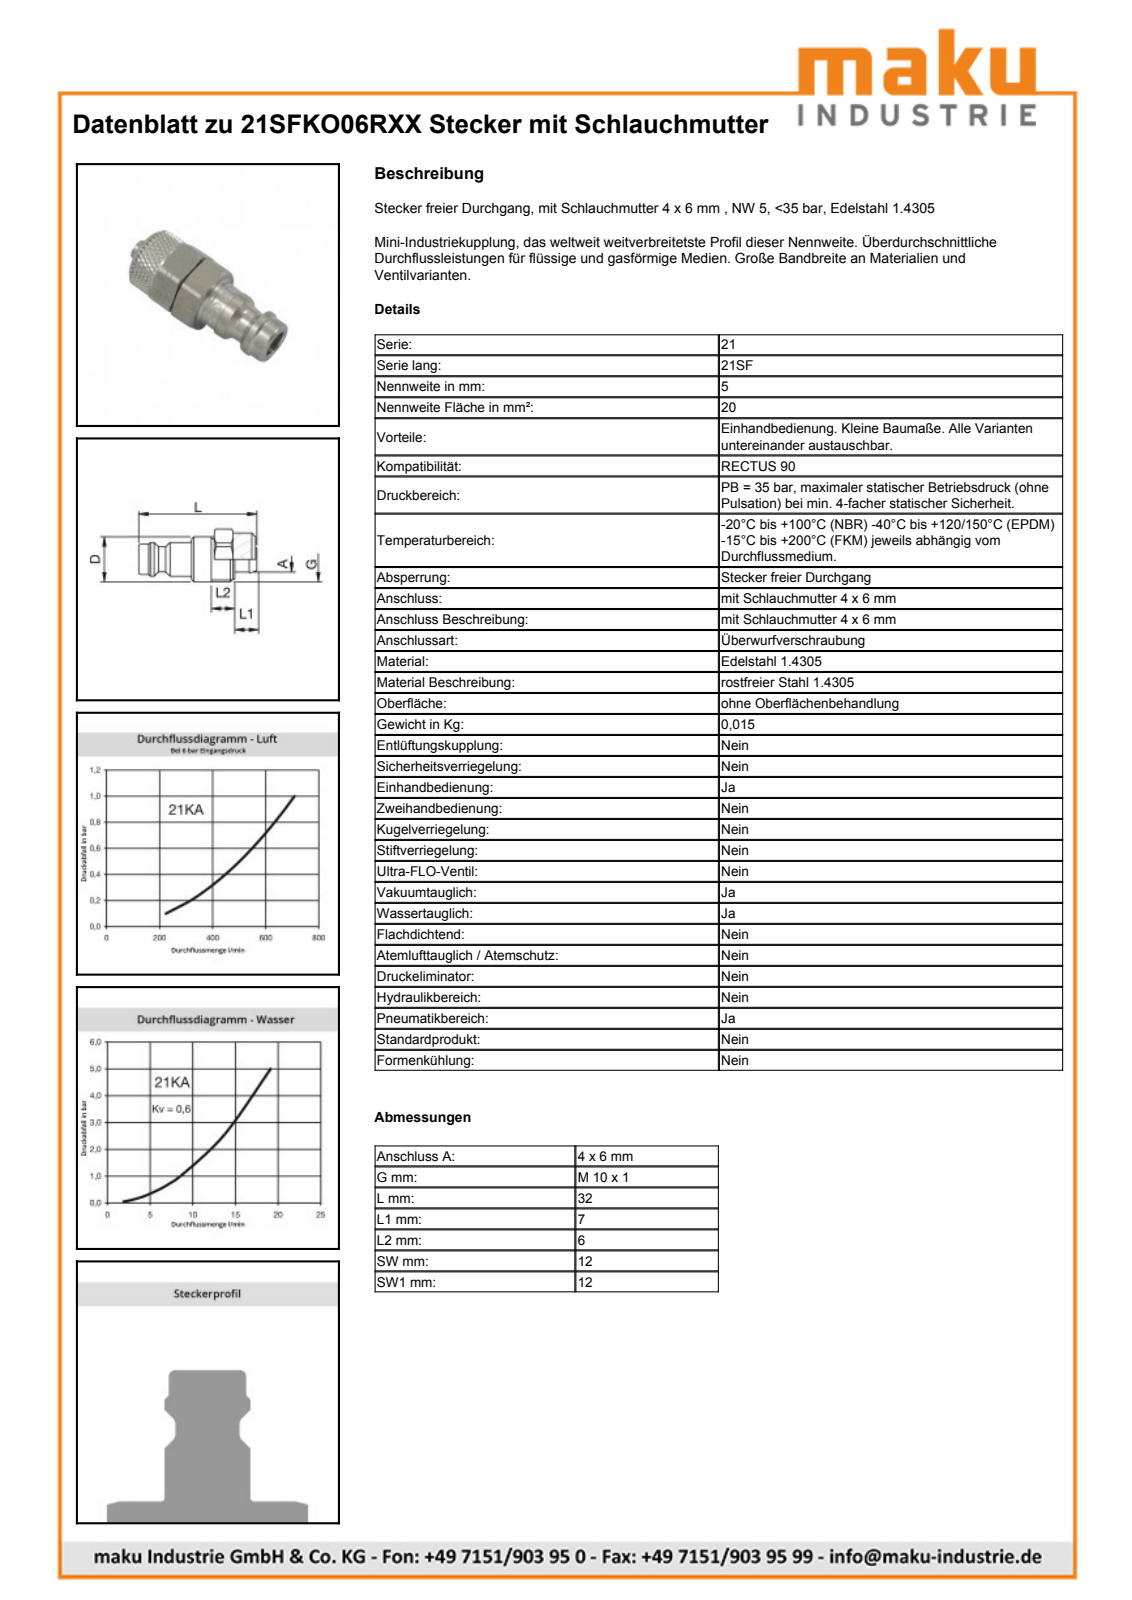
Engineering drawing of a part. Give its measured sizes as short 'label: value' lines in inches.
name: D108466; D106317; D102670
written by: Autodesk Inventor 2013 (AUTOMOTIVE_DESIGN)
unit: in
bodies: 2 solids, 60 faces (11 planar, 18 cylindrical, 31 other)
size: 1.24 × 0.531 × 0.493
volume: 0.117 in³; area: 3.464 in²
holes: 1× ⌀0.13, 1× ⌀0.197, 1× ⌀0.244, 1× ⌀0.351
bosses: 1× ⌀0.472, 1× ⌀0.394, 1× ⌀0.354, 1× ⌀0.339, 1× ⌀0.319, 1× ⌀0.262, 1× ⌀0.187
rounds: 1× R0.266
face distances: 0.472, 0.433, 0.203, 0.23, 1.215, 1.012, 0.782, 0.025, 0.228, 0.458
